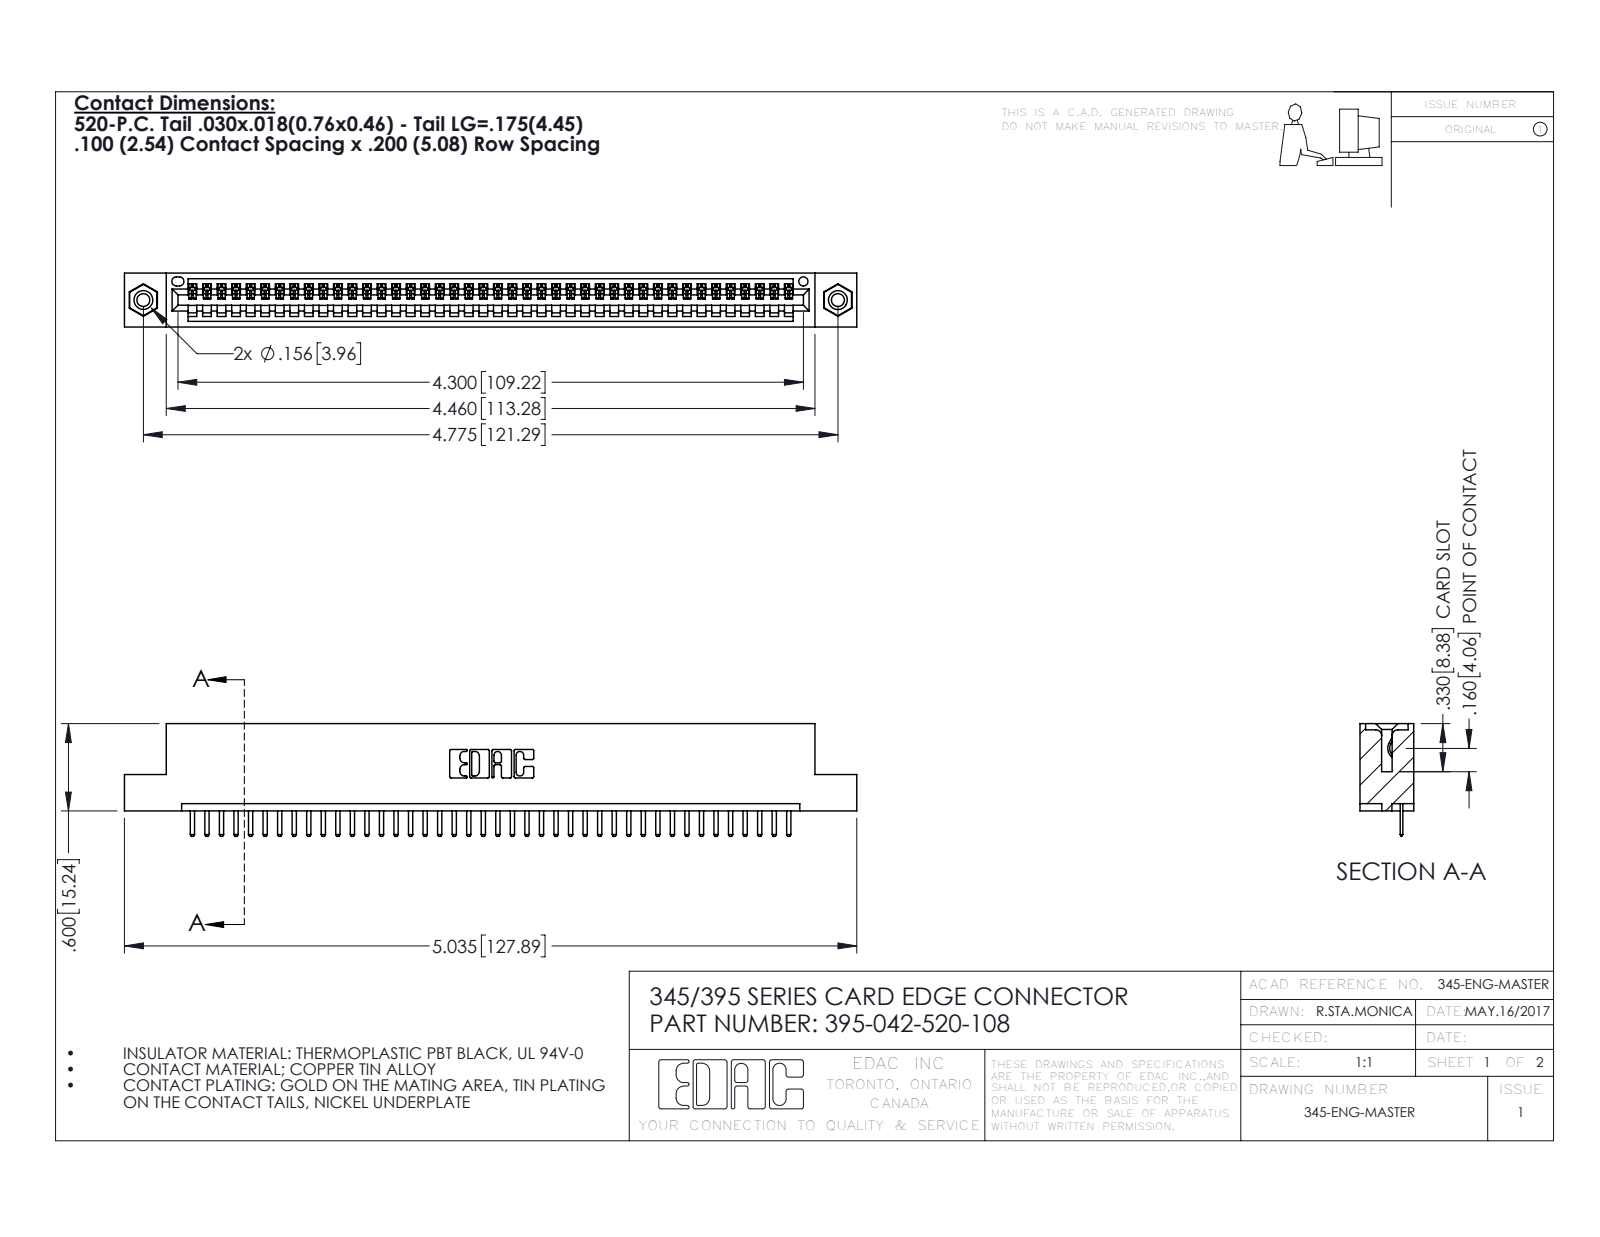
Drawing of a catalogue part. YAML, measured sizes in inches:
part_name: "345 Part_Flush Mounting Lugs - 0.156 Dia-TI; 345-250-001_345-250-003-102; 345-292-001_345-293-120; 395-042-520-108"
step_written_by: "SolidWorks 2016 (CONFIG_CONTROL_DESIGN)"
units: inches
bodies: {solids: 45, faces: 2790, planar: 1876, cylindrical: 898, other: 16}
overall_size: [5.035, 0.775, 0.37]
volume: 0.733
surface_area: 24.18
round_holes:
  - {diameter: 0.089, count: 2}
  - {diameter: 0.125, count: 2}
  - {diameter: 0.156, count: 2}
  - {diameter: 0.064, count: 1}
round_bosses_or_shafts:
  - {diameter: 0.155, count: 2}
partial_cylinders:
  - {radius: 0.01, count: 86}
  - {radius: 0.006, count: 84}
  - {radius: 0.01, count: 22}
  - {radius: 0.007, count: 6}
  - {radius: 0.031, count: 6}
  - {radius: 0.026, count: 3}
  - {radius: 0.031, count: 2}
  - {radius: 0.04, count: 2}
face_to_face_distances: [0.072, 0.298, 0.37, 0.2, 0.098, 0.272, 0.025, 0.225, 0.072, 0.149]
hole_center_spacings: [0.27, 4.539, 4.775]
